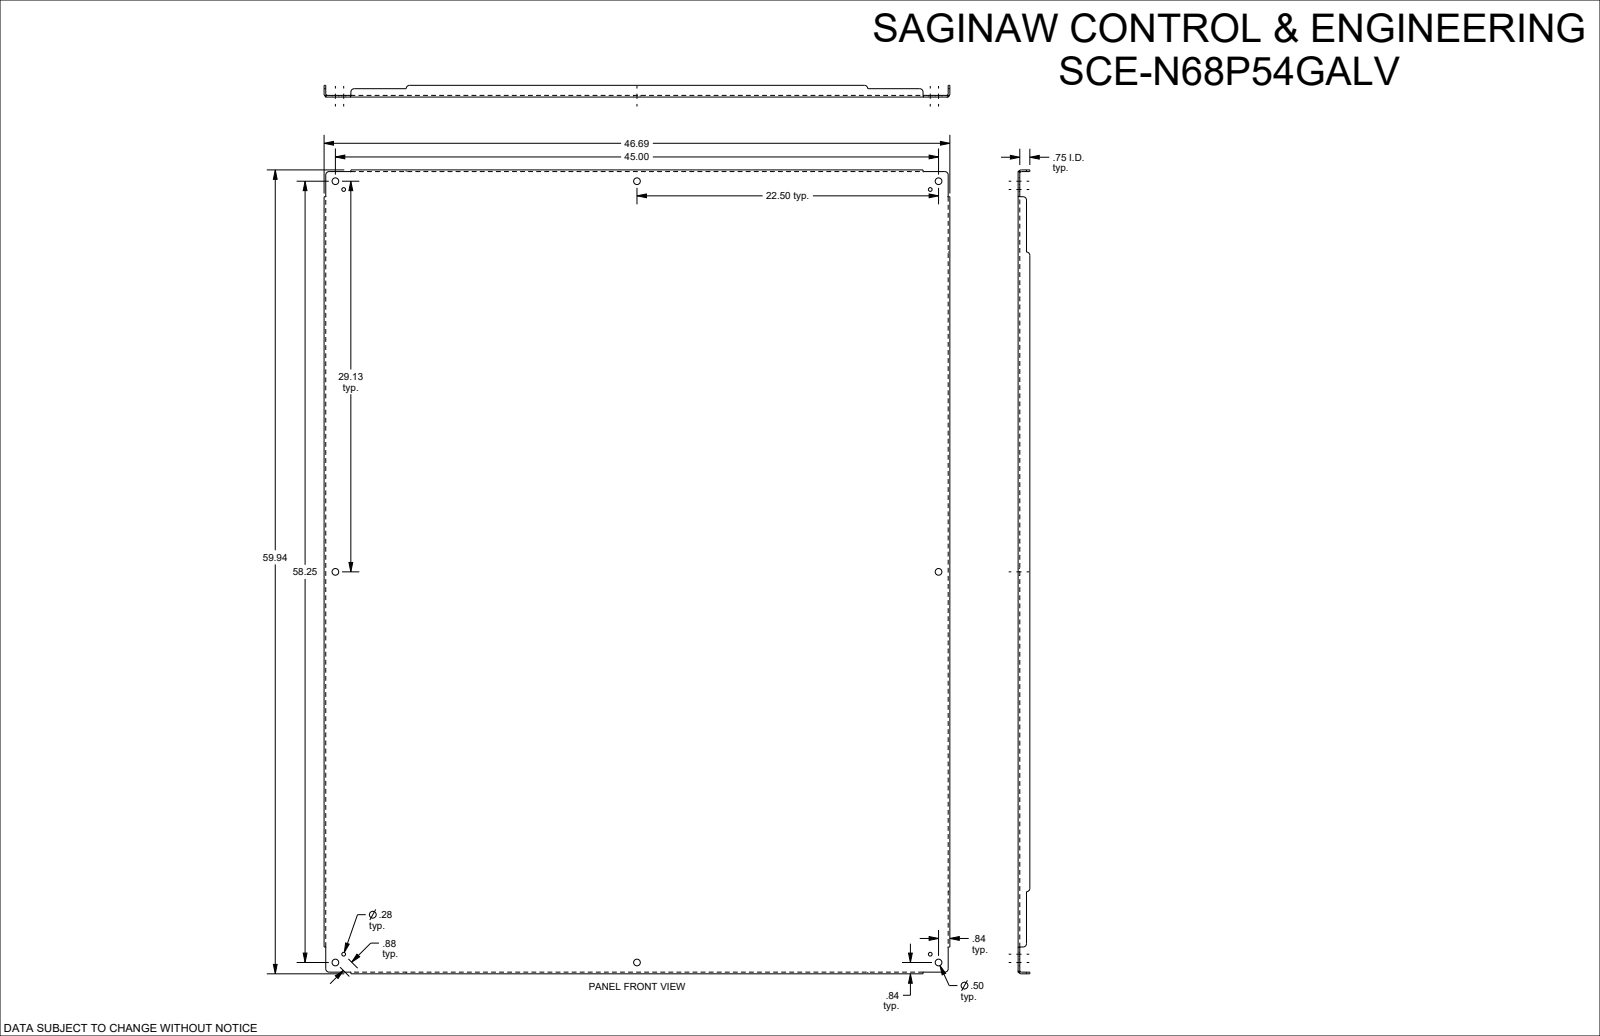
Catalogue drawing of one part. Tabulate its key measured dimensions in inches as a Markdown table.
| quantity | value |
| --- | --- |
| part name | SCE-N68P54GALV |
| STEP written by | SolidWorks 2023 (AUTOMOTIVE_DESIGN) |
| units | inches |
| bodies | 1 solid, 122 faces (46 planar, 52 cylindrical, 24 other) |
| overall size | 59.938 × 46.688 × 0.875 |
| volume | 364.9 in³ |
| surface area | 5 868 in² |
| round holes (diameter × count) | 0.5 × 8, 0.281 × 4 |
| partial cylindrical surfaces (radius × count) | 0.25 × 12, 0.112 × 4, 0.237 × 4 |
| main face-to-face distances | 0.125, 46.563, 0.125, 59.813, 46.438, 46.687, 59.687, 59.938, 0.75, 0.875 |
| hole center spacings | 0.875, 21.89, 22.5, 28.513, 29.125, 36.804, 44.385, 52.747 |
